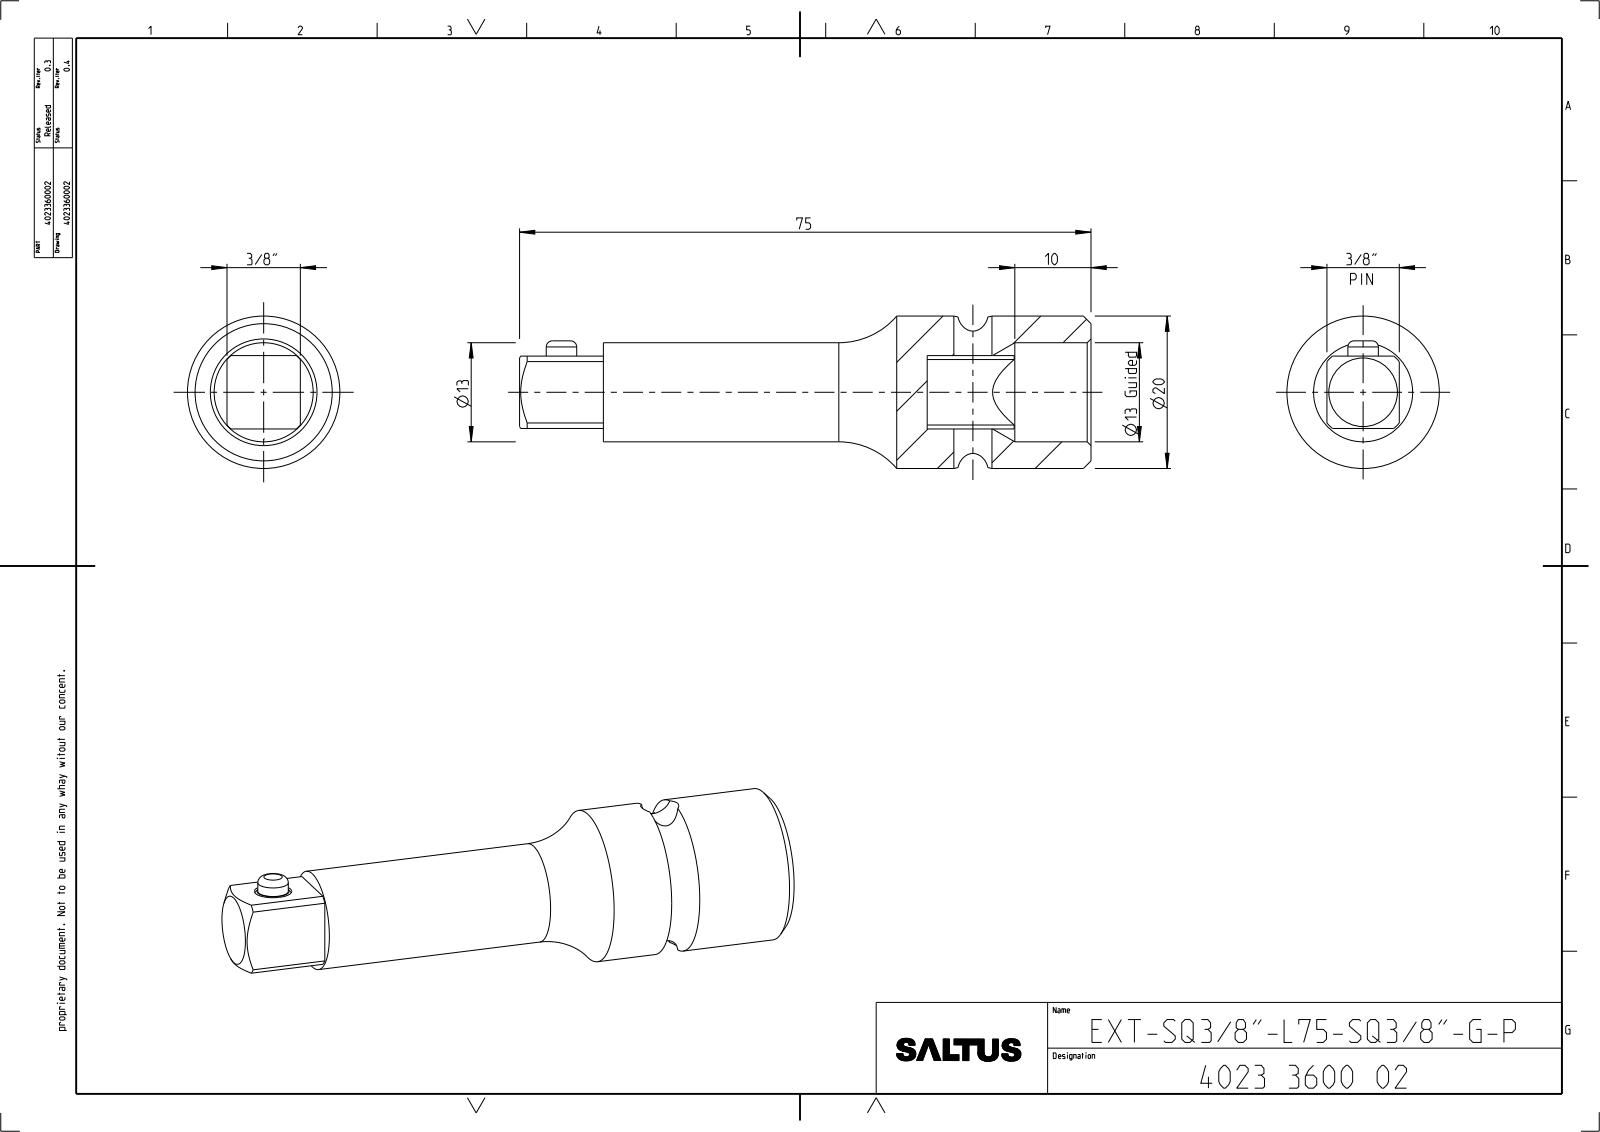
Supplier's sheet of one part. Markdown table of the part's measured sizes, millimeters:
| quantity | value |
| --- | --- |
| part name | 4023360002 |
| STEP written by | CREO PARAMETRIC BY PTC INC, 2022414 (CONFIG_CONTROL_DESIGN) |
| units | millimeters |
| bodies | 2 solids, 61 faces (17 planar, 26 cylindrical, 18 other) |
| overall size | 75 × 20 × 20 |
| volume | 11 543 mm³ |
| surface area | 5 231 mm² |
| round holes (diameter × count) | 4.9 × 1, 5 × 1, 13 × 1 |
| round bosses / shafts (diameter × count) | 20 × 1, 4.8 × 1, 4 × 1 |
| partial cylindrical surfaces (radius × count) | 6.22 × 1, 6.45 × 1 |
| main face-to-face distances | 9.56, 9.5, 9.62, 21.5, 75, 53.5, 64, 42.5, 11, 3.25 |
| hole center spacings | 54 |
